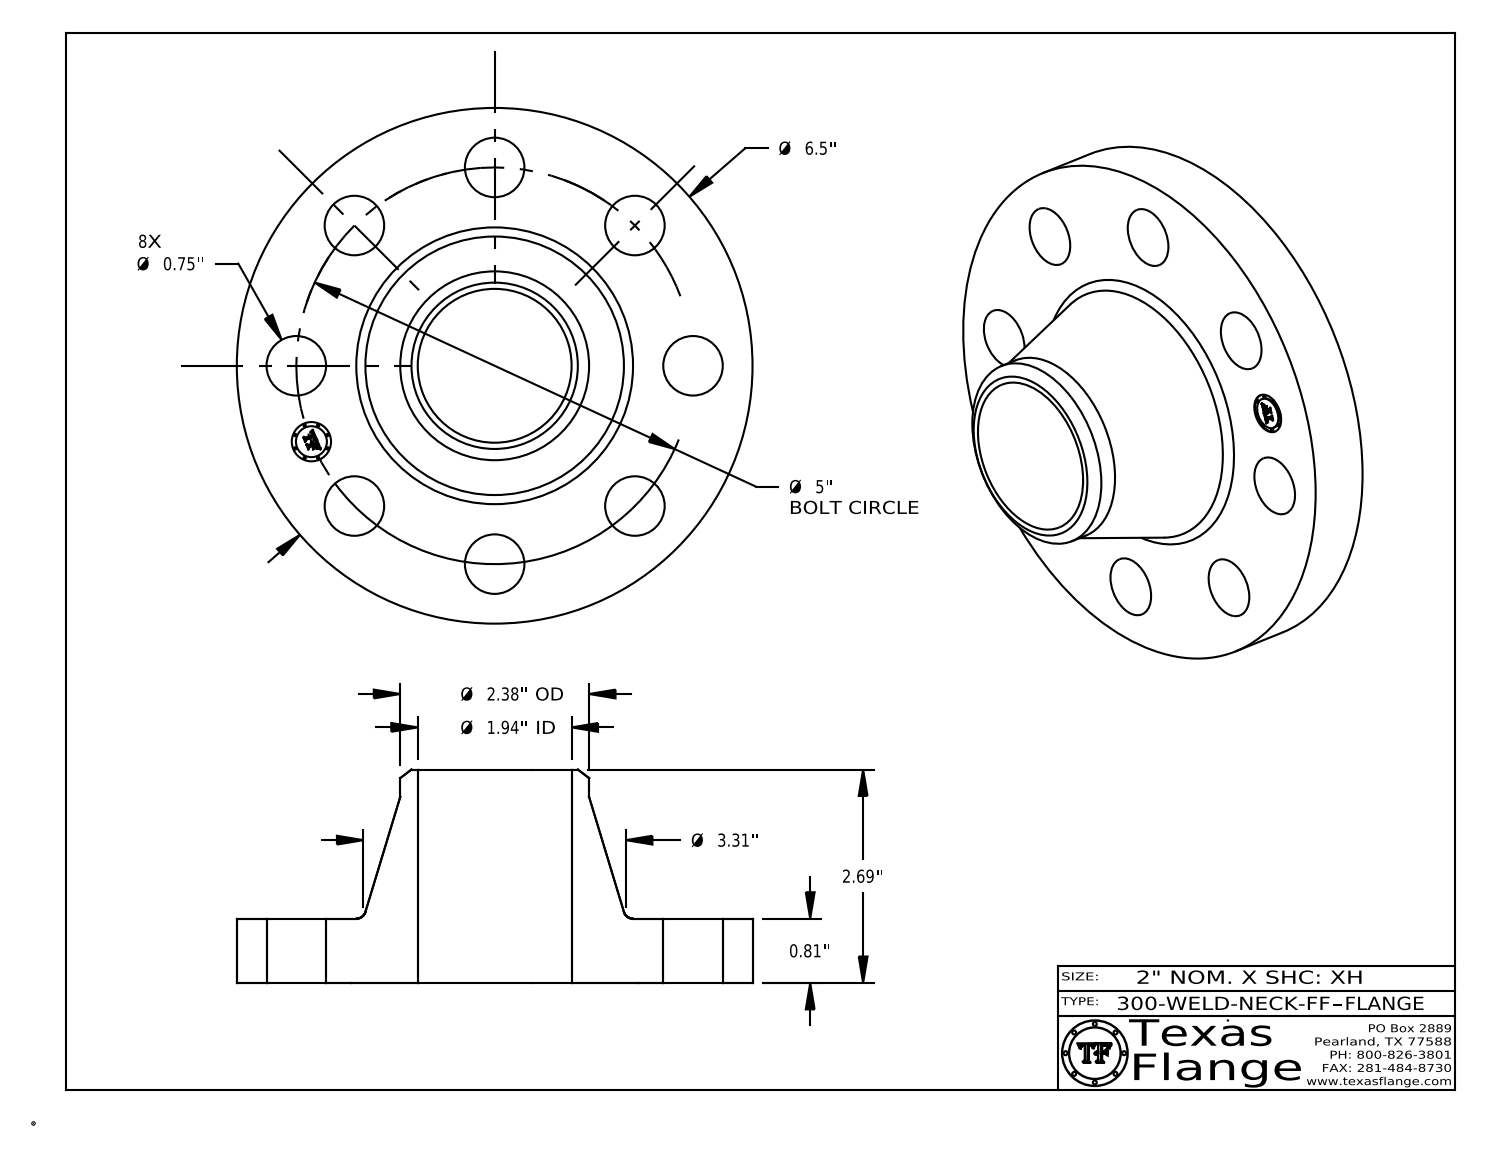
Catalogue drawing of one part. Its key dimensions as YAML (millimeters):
part_name: "300-WELD-NECK-FF"
step_written_by: "CATIA V5 STEP AP214 (AUTOMOTIVE_DESIGN)"
units: millimeters
bodies: {solids: 1, faces: 417, planar: 369, cylindrical: 42, other: 6}
overall_size: [165.1, 165.1, 68.3]
volume: 449200
surface_area: 73290
round_holes:
  - {diameter: 19.1, count: 8}
  - {diameter: 12.6, count: 1}
  - {diameter: 49.3, count: 1}
round_bosses_or_shafts:
  - {diameter: 0.8, count: 8}
  - {diameter: 165.1, count: 1}
  - {diameter: 60.5, count: 1}
  - {diameter: 9.9, count: 1}
face_to_face_distances: [20.6, 68.3, 47.8, 20.2, 0.4, 48.1, 3.8, 3.7, 0.7, 2.4]
hole_center_spacings: [63.5, 48.6, 89.8, 117.3, 127, 24.8, 70.6, 105.6]
